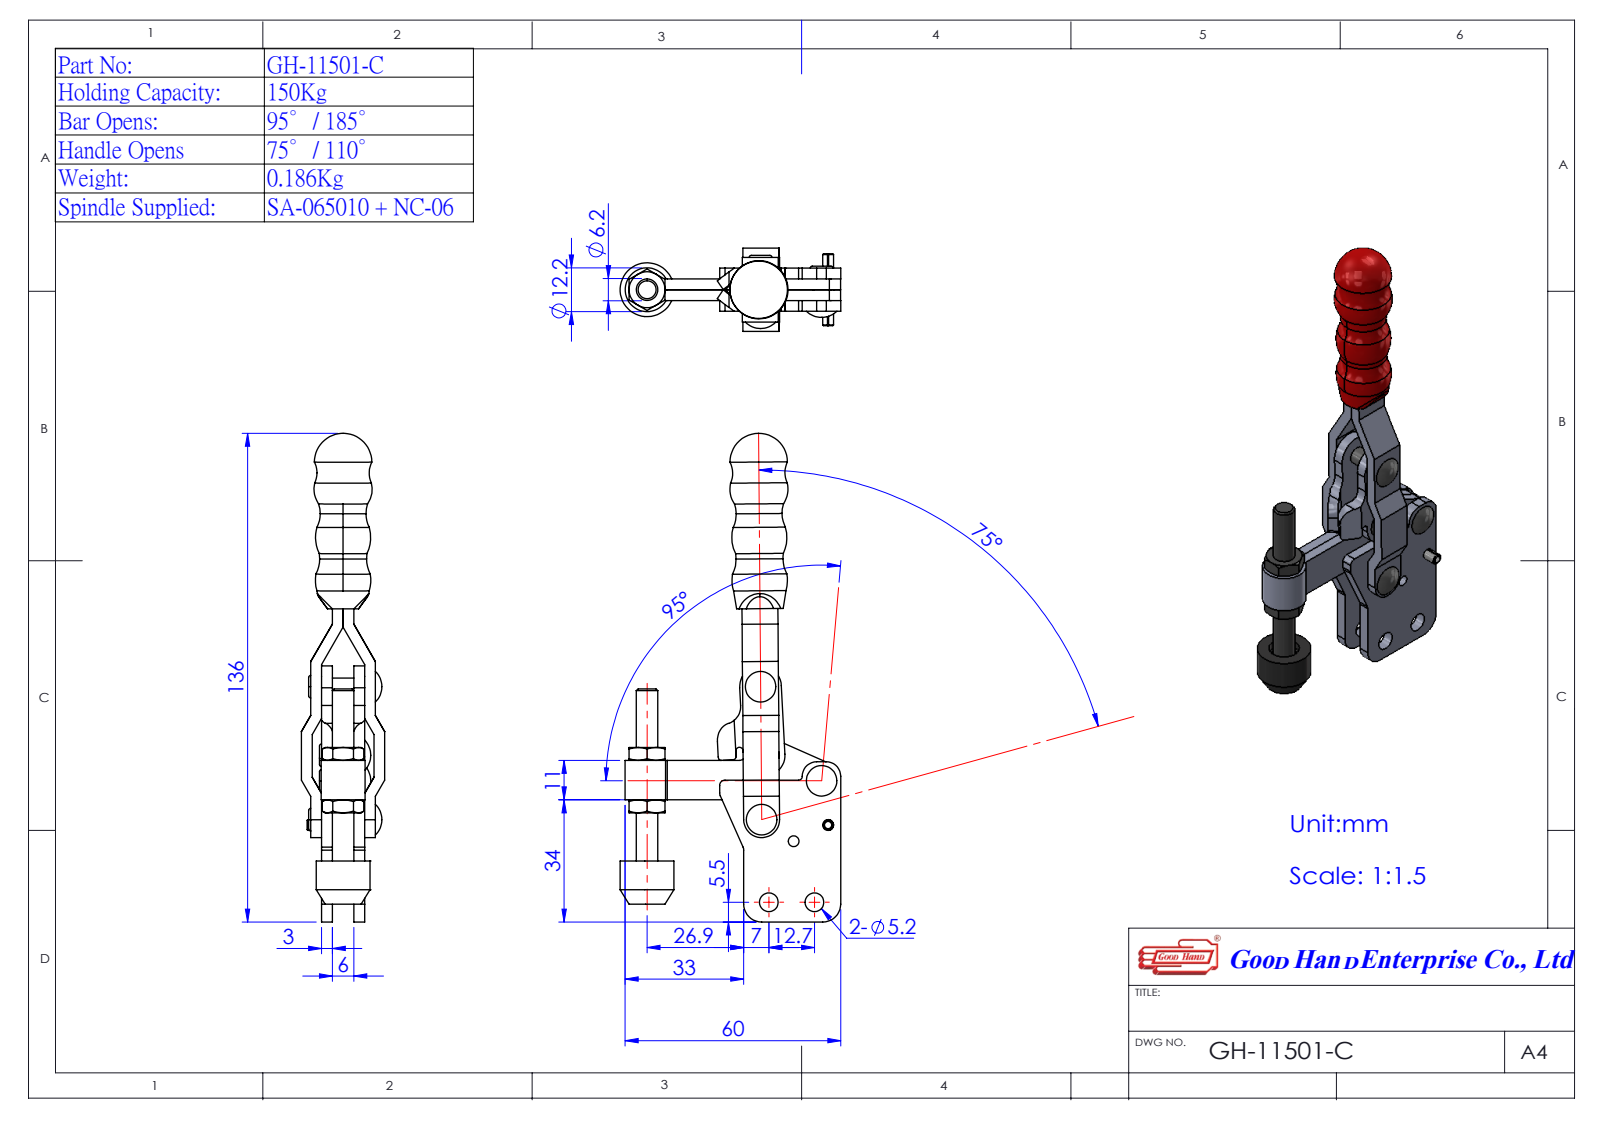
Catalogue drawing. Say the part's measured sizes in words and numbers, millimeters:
The part is named "GH-11501-C(簡化)-1; Group2^GH-11501-C(簡化)-1; Group4^GH-11501-B(簡化)-1; GH-SA-065010-1^GH-11501-C(簡化)-1 (+3 more)". Its 3-D file was written by "SolidWorks 2016 (AUTOMOTIVE_DESIGN)". It is 13 solids with 306 faces: 124 planar, 102 cylindrical and 80 other. Overall it measures 136.01 by 61.4 by 24.5 millimeters. Its volume is 29 422 cubic millimeters and its surface area 21 432 square millimeters. Round holes: 6 of diameter 3, 2 of diameter 5.3, 1 of diameter 5, 1 of diameter 6, 1 of diameter 6.2, 1 of diameter 12. Round bosses or shafts: 1 of diameter 15, 1 of diameter 7.5. Partial cylindrical surfaces (rounded edges, fillets, slot ends): 5 of radius 1, 4 of radius 5, 2 of radius 0.5, 2 of radius 2, 2 of radius 3.5, 2 of radius 4, 2 of radius 5.3, 2 of radius 5.8. The main face-to-face distances are 3, 6, 9, 12, 14.6, 2.6, 11.6, 5.6, 8.6, 17.6. The hole center spacings are 10.52, 10.73, 12.63, 12.7, 17.5, 17.91, 17.96, 18.35.
